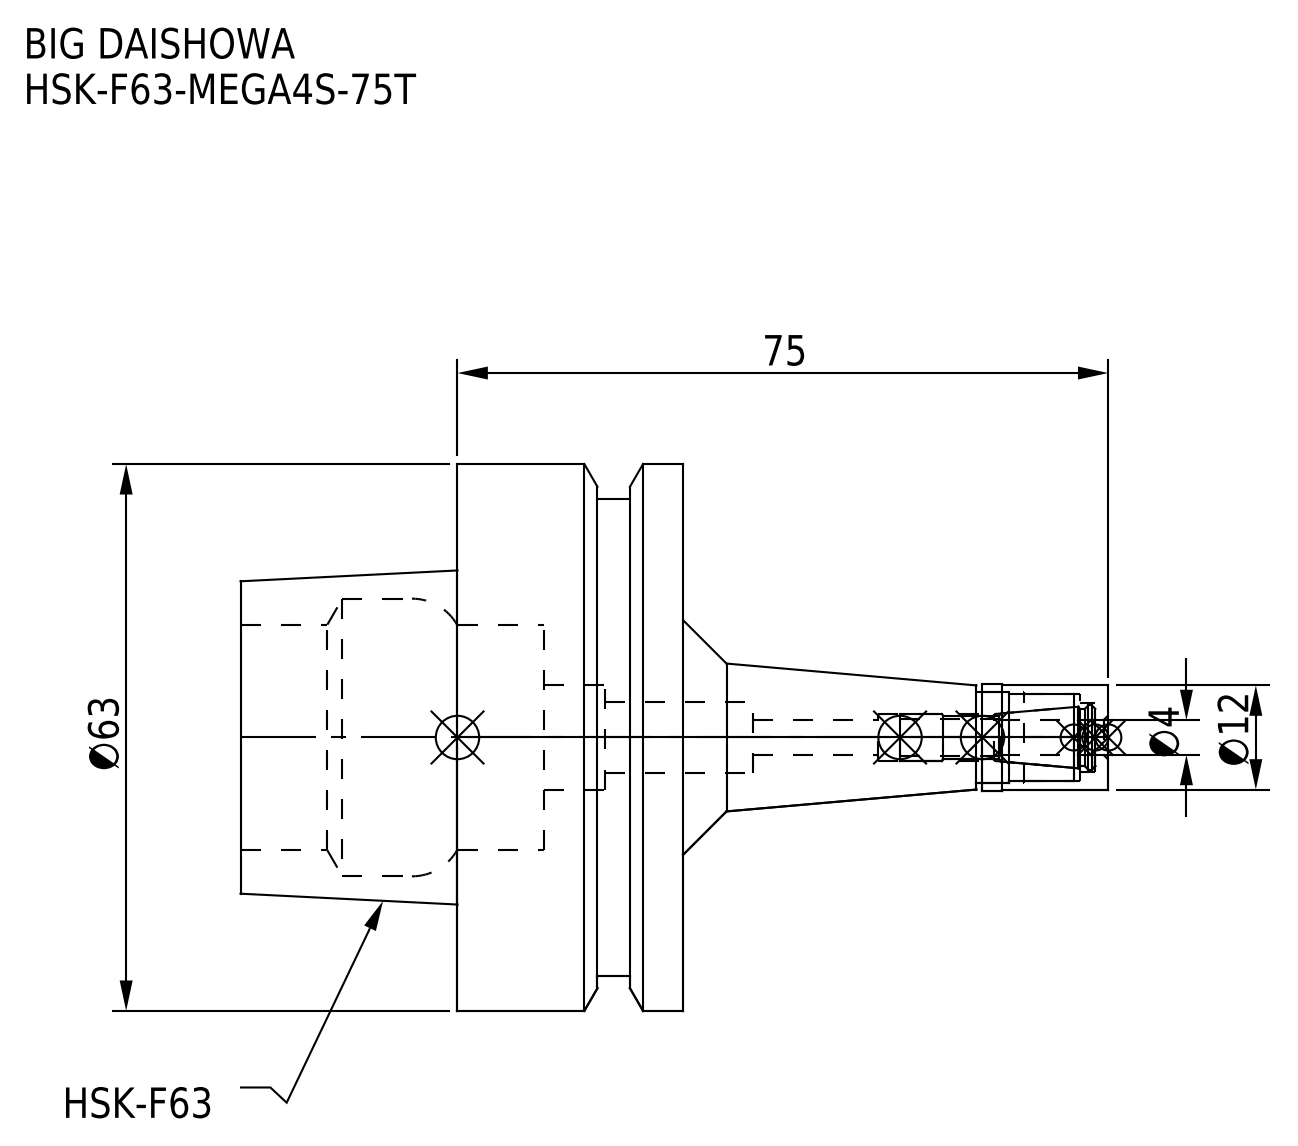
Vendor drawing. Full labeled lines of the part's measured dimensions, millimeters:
Part name (STEP PRODUCT): HSK-F63-MEGA4S-75T-040.stp; DXF_TEMP_ASSY_ASM_4_ASM.stp; HSK-F63-MEGA4S-75T-040-FreeParts; MGN4S_1.stp (+3 more)
STEP written by: SolidWorks 2019 (CONFIG_CONTROL_DESIGN)
Units: millimetres
Bodies: 2 solids, 74 faces (18 planar, 38 cylindrical, 18 other)
Overall size (bounding box): 100 × 63 × 63
Volume: 88 617 mm³ · Surface area: 22 598 mm²
Round holes (diameter × count): ⌀4.1 ×1, ⌀5.4 ×1, ⌀8 ×1, ⌀8.25 ×1, ⌀10 ×1, ⌀10.5 ×1, ⌀12 ×1, ⌀26 ×1, ⌀32 ×1
Round bosses / shafts (diameter × count): ⌀63 ×1, ⌀55 ×1, ⌀12.3 ×1
Main face-to-face distances: 26, 25, 51, 16.05, 9.95, 34.95, 9.88, 6.17, 16.12, 41.12
